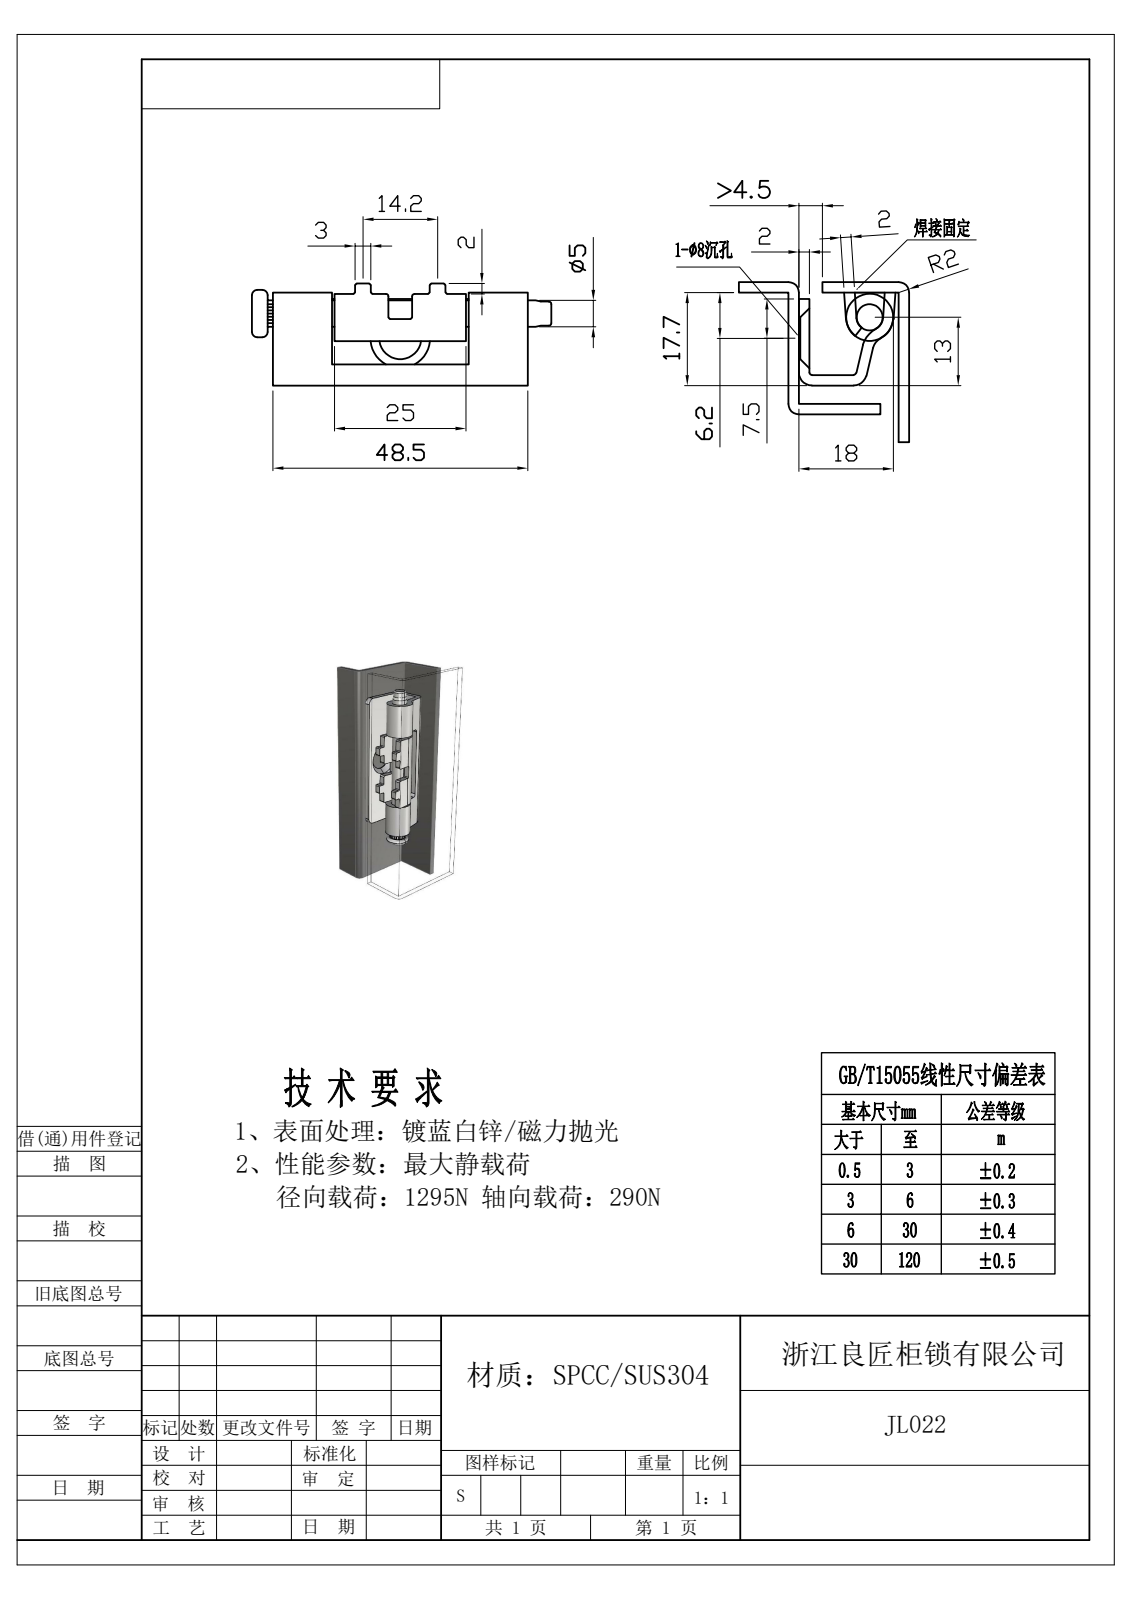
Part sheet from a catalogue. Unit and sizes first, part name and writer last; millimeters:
Units: millimetres
Overall size (bounding box): 57 × 19.45 × 18.47
Round holes (diameter × count): ⌀5 ×1, ⌀8 ×1
Round bosses / shafts (diameter × count): ⌀9 ×1, ⌀4.8 ×1, ⌀4.4 ×1
Partial cylindrical surfaces — rounded edges, fillets, slot ends (radius × count): R0.3 ×12, R0.5 ×4, R1 ×2, R2.5 ×2, R2.55 ×1, R2.65 ×1, R3 ×1, R4.55 ×1
Main face-to-face distances: 2, 48.5, 1.99, 16.5, 14.5, 11.25, 37.25, 11.75, 36.75, 0.5
Volume: 5 781 mm³ · Surface area: 6 487 mm²
Bodies: 3 solids, 154 faces (54 planar, 70 cylindrical, 30 other)
STEP written by: Rhino 8.5 (CONFIG_CONTROL_DESIGN)
